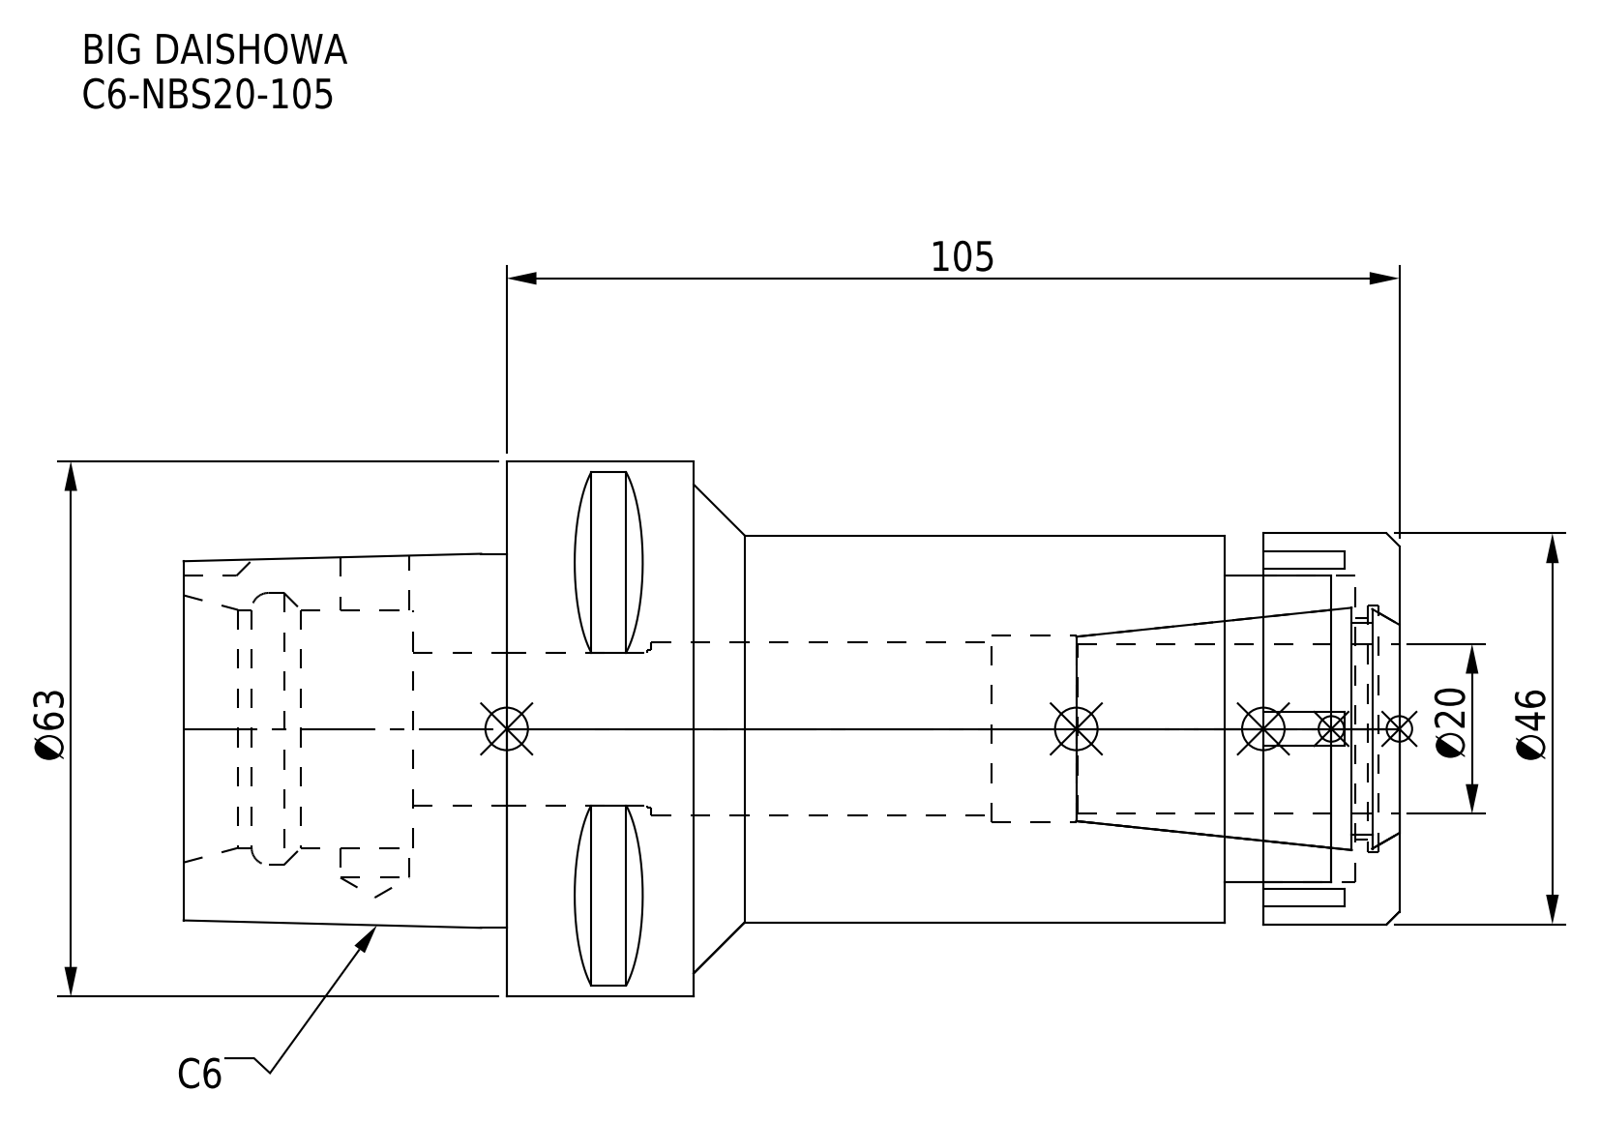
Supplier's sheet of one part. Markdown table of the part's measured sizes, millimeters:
| quantity | value |
| --- | --- |
| part name | C6-NBS20-105; NBN20_1.stp; C6-NBS20-105-200_ASM.stp; C6-NBS20-105.stp (+3 more) |
| STEP written by | SolidWorks 2019 (CONFIG_CONTROL_DESIGN) |
| units | millimeters |
| bodies | 2 solids, 112 faces (61 planar, 33 cylindrical, 18 other) |
| overall size | 143 × 63 × 63 |
| volume | 193 946 mm³ |
| surface area | 41 679 mm² |
| round holes (diameter × count) | 8.1 × 1, 18 × 1, 18.5 × 1, 20.3 × 1, 22 × 1, 26 × 1, 28 × 1, 29 × 1, 32 × 1, 36 × 1 |
| round bosses / shafts (diameter × count) | 63 × 1, 46 × 1, 45.5 × 1 |
| partial cylindrical surfaces (radius × count) | 5 × 1 |
| main face-to-face distances | 105, 8, 20.5, 84.5, 16, 4.5, 89, 22, 67, 83 |
